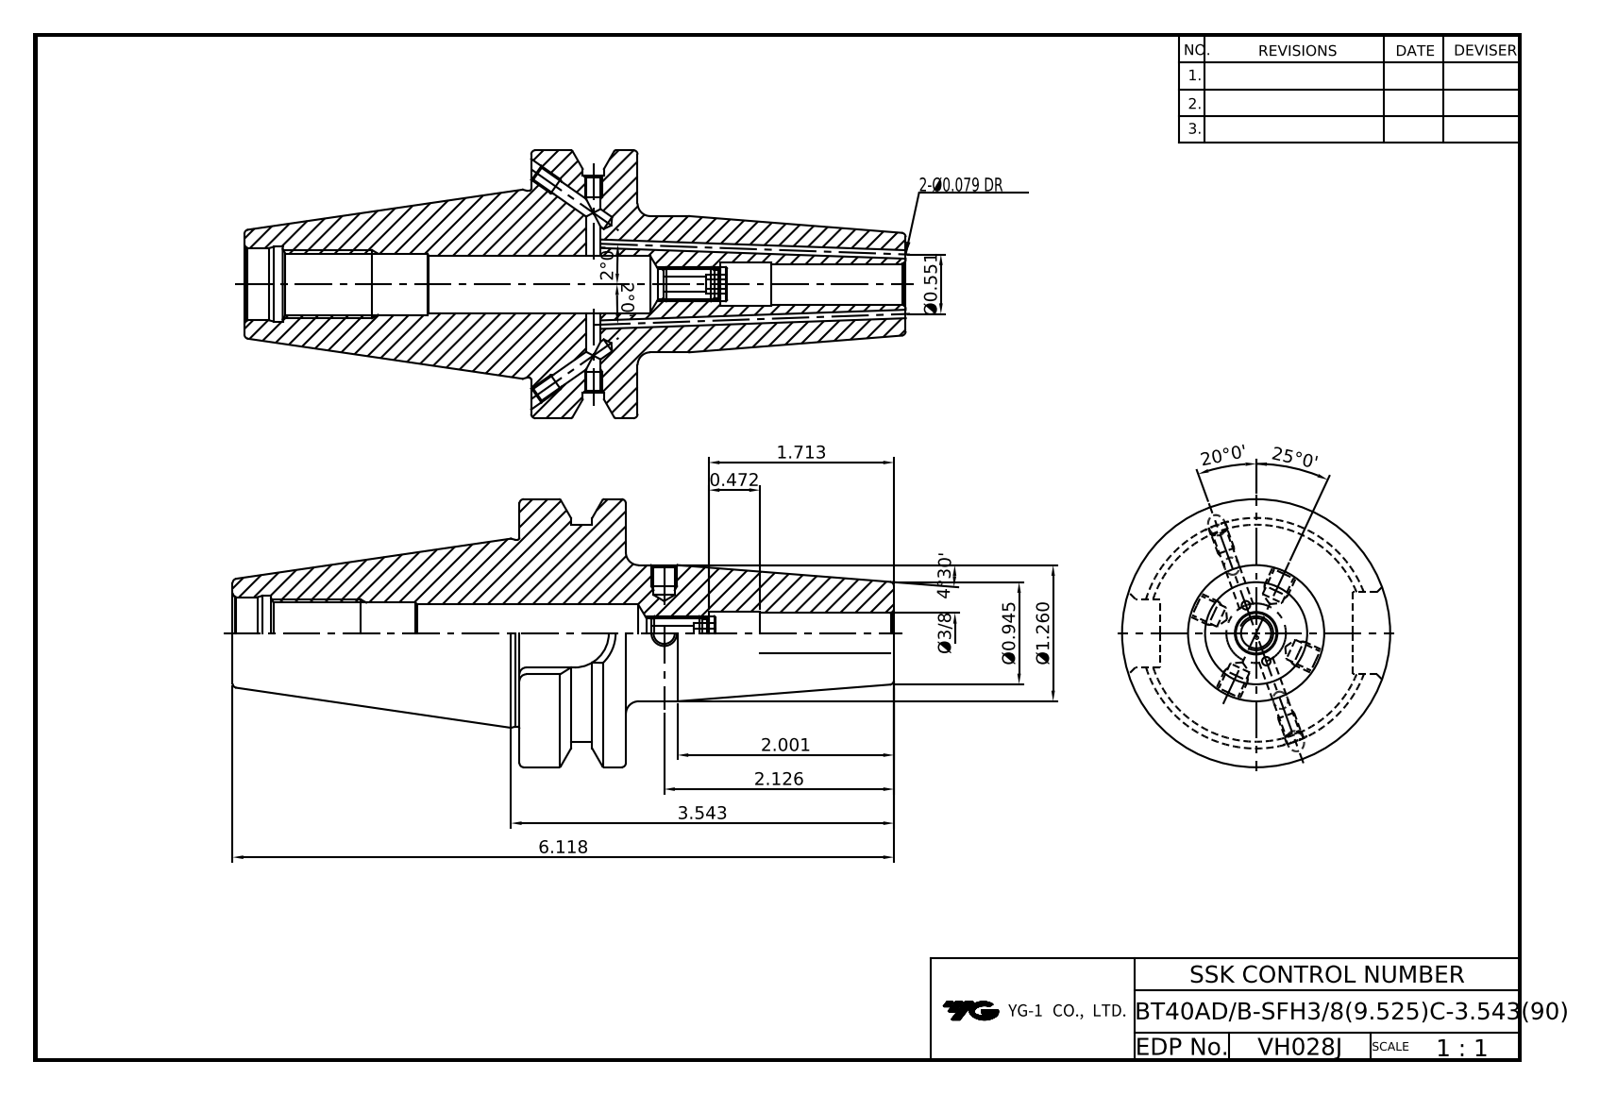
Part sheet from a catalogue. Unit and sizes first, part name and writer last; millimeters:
Units: millimetres
Overall size (bounding box): 155.4 × 63 × 63
Round holes (diameter × count): ⌀3.24 ×4, ⌀4 ×4, ⌀2.5 ×2, ⌀6.92 ×1, ⌀9.53 ×1, ⌀10.72 ×1, ⌀13.5 ×1, ⌀13.84 ×1, ⌀17 ×1, ⌀17.6 ×1
Round bosses / shafts (diameter × count): ⌀63 ×1, ⌀51 ×1, ⌀44 ×1, ⌀32 ×1
Partial cylindrical surfaces — rounded edges, fillets, slot ends (radius × count): R8.05 ×1
Main face-to-face distances: 25, 45.2, 88, 63, 17.1, 7.9, 70.9, 12.1, 5, 12.9
Volume: 155 263 mm³ · Surface area: 31 179 mm²
Bodies: 1 solid, 76 faces (23 planar, 30 cylindrical, 23 other)
Part name (STEP PRODUCT): LO-BT40ADB-SFH9.525C-90
STEP written by: Autodesk Inventor 2024 (AUTOMOTIVE_DESIGN)
